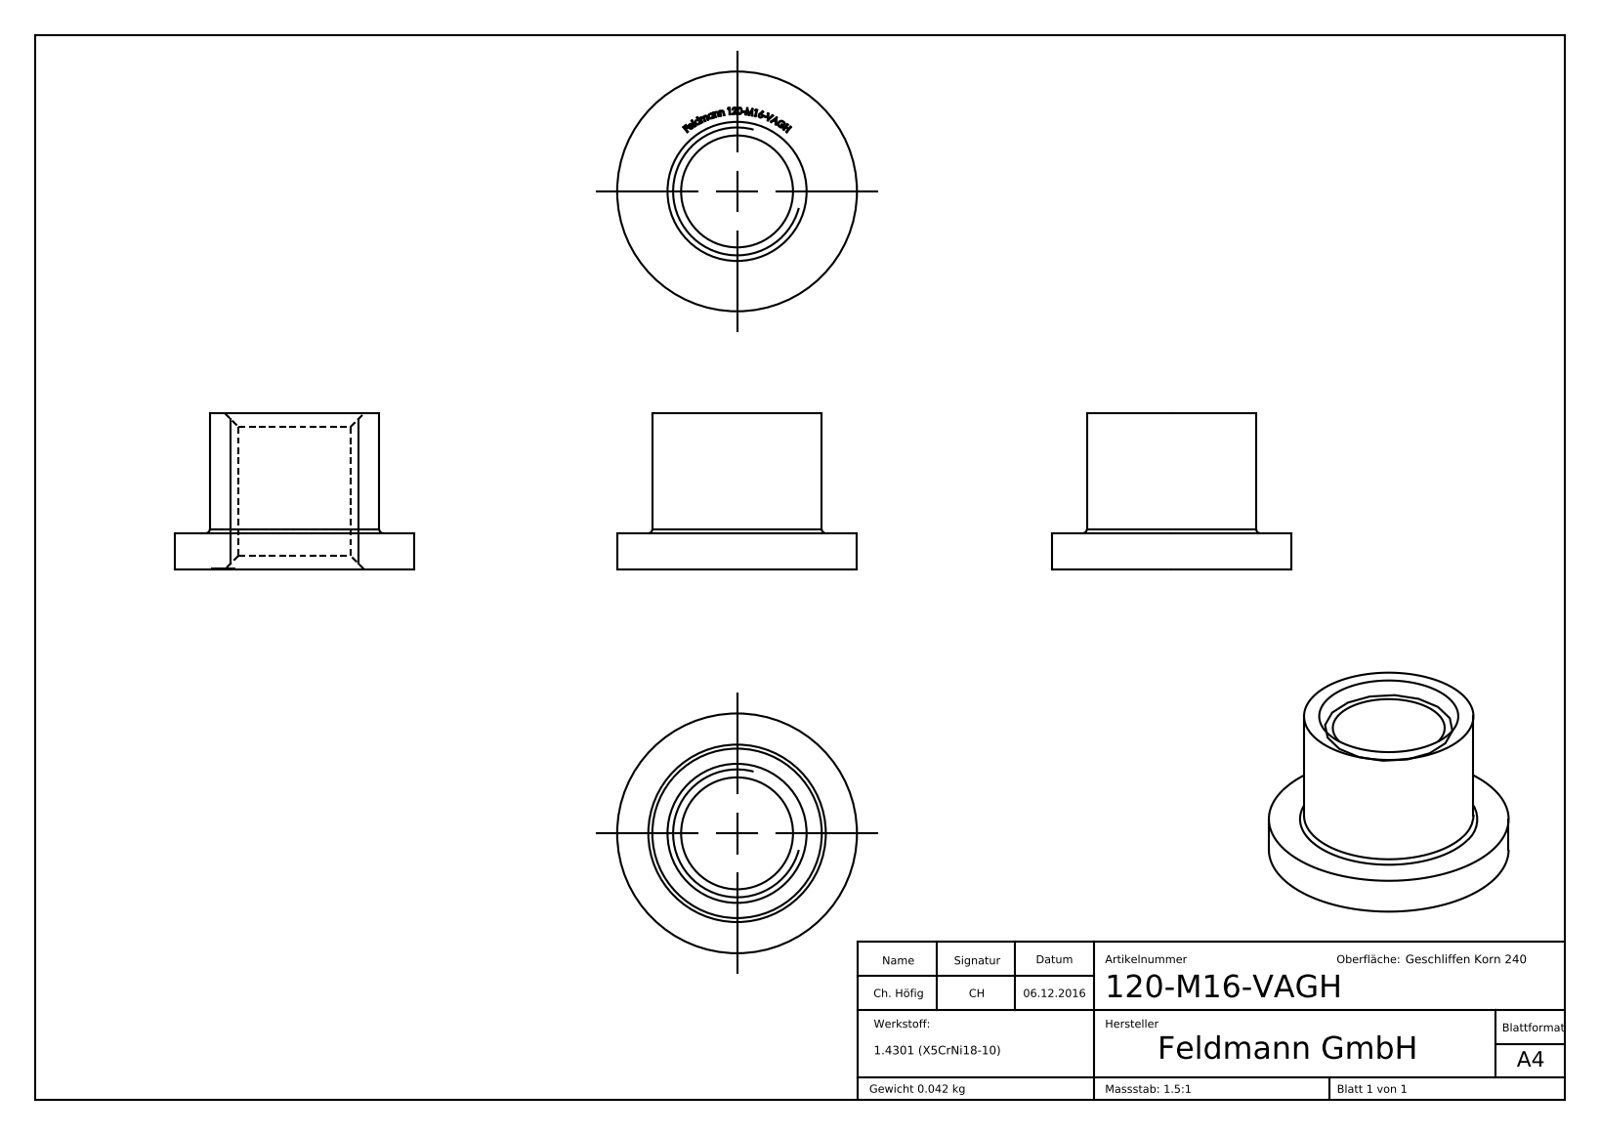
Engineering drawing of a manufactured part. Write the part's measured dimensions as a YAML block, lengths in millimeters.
part_name: "120-M16-VAGH"
step_written_by: "SolidWorks 2015 (CONFIG_CONTROL_DESIGN)"
units: millimeters
bodies: {solids: 1, faces: 252, planar: 159, cylindrical: 6, other: 87}
overall_size: [30, 30, 19.5]
volume: 5340
surface_area: 3299
round_holes:
  - {diameter: 14, count: 1}
round_bosses_or_shafts:
  - {diameter: 30, count: 1}
  - {diameter: 21.2, count: 1}
face_to_face_distances: [4.5, 19.5, 15, 4.4, 19.4, 0.49, 0.4, 0.41, 0.57, 0.32]
